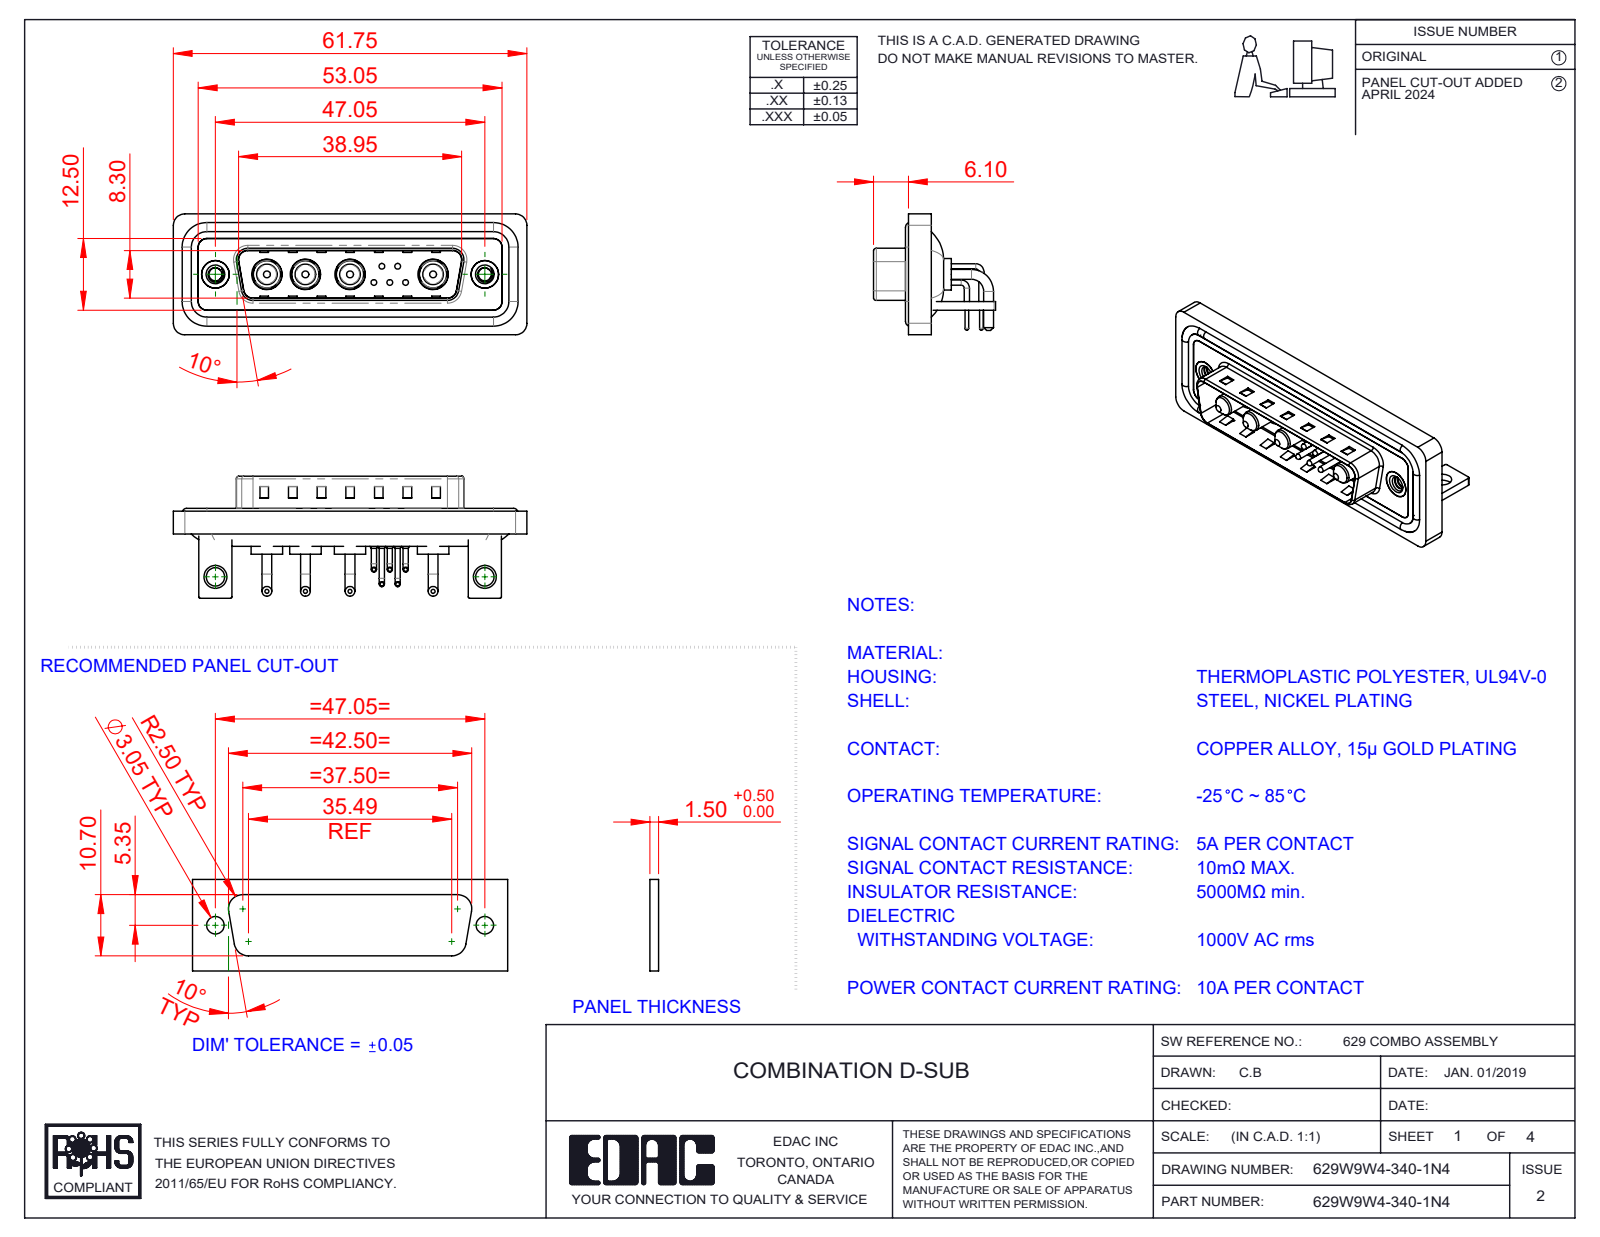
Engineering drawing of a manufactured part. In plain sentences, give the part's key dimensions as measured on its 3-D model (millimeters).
The part is named "629Combo Waterproof Housing_25 Contacts; 629Combo Contact Row 2; 629Combo Shell Front_25 Contacts; 629Combo Shell Rear_25 Contacts (+6 more)". Its 3-D file was written by "SolidWorks 2023 (CONFIG_CONTROL_DESIGN)". It is 22 solids with 1245 faces: 589 planar, 470 cylindrical and 186 other. Overall it measures 61.75 by 21.3 by 21.1 millimeters. Its volume is 7 750 cubic millimeters and its surface area 12 760 square millimeters. Round holes: 5 of diameter 0.75, 5 of diameter 1.6, 5 of diameter 2, 4 of diameter 4.85, 4 of diameter 5.3, 2 of diameter 2.26, 2 of diameter 3.2, 2 of diameter 4, 2 of diameter 4.8, 2 of diameter 5. Round bosses or shafts: 10 of diameter 0.9, 8 of diameter 1.7, 5 of diameter 1.5, 5 of diameter 1, 5 of diameter 0.65, 4 of diameter 5.5, 4 of diameter 5.2, 4 of diameter 4.75. Partial cylindrical surfaces (rounded edges, fillets, slot ends): 19 of radius 2, 18 of radius 1.5, 16 of radius 0.25, 9 of radius 0.5, 8 of radius 1.6, 5 of radius 1.01, 4 of radius 0.6, 4 of radius 0.65. The main face-to-face distances are 0.4, 1.5, 0.8, 2.9, 2.1, 1.1, 3.7, 4.1, 4.5, 1.6. The hole center spacings are 3.16, 2.77, 5.04, 14.5, 47.05, 2.78, 4.4, 4.41.
